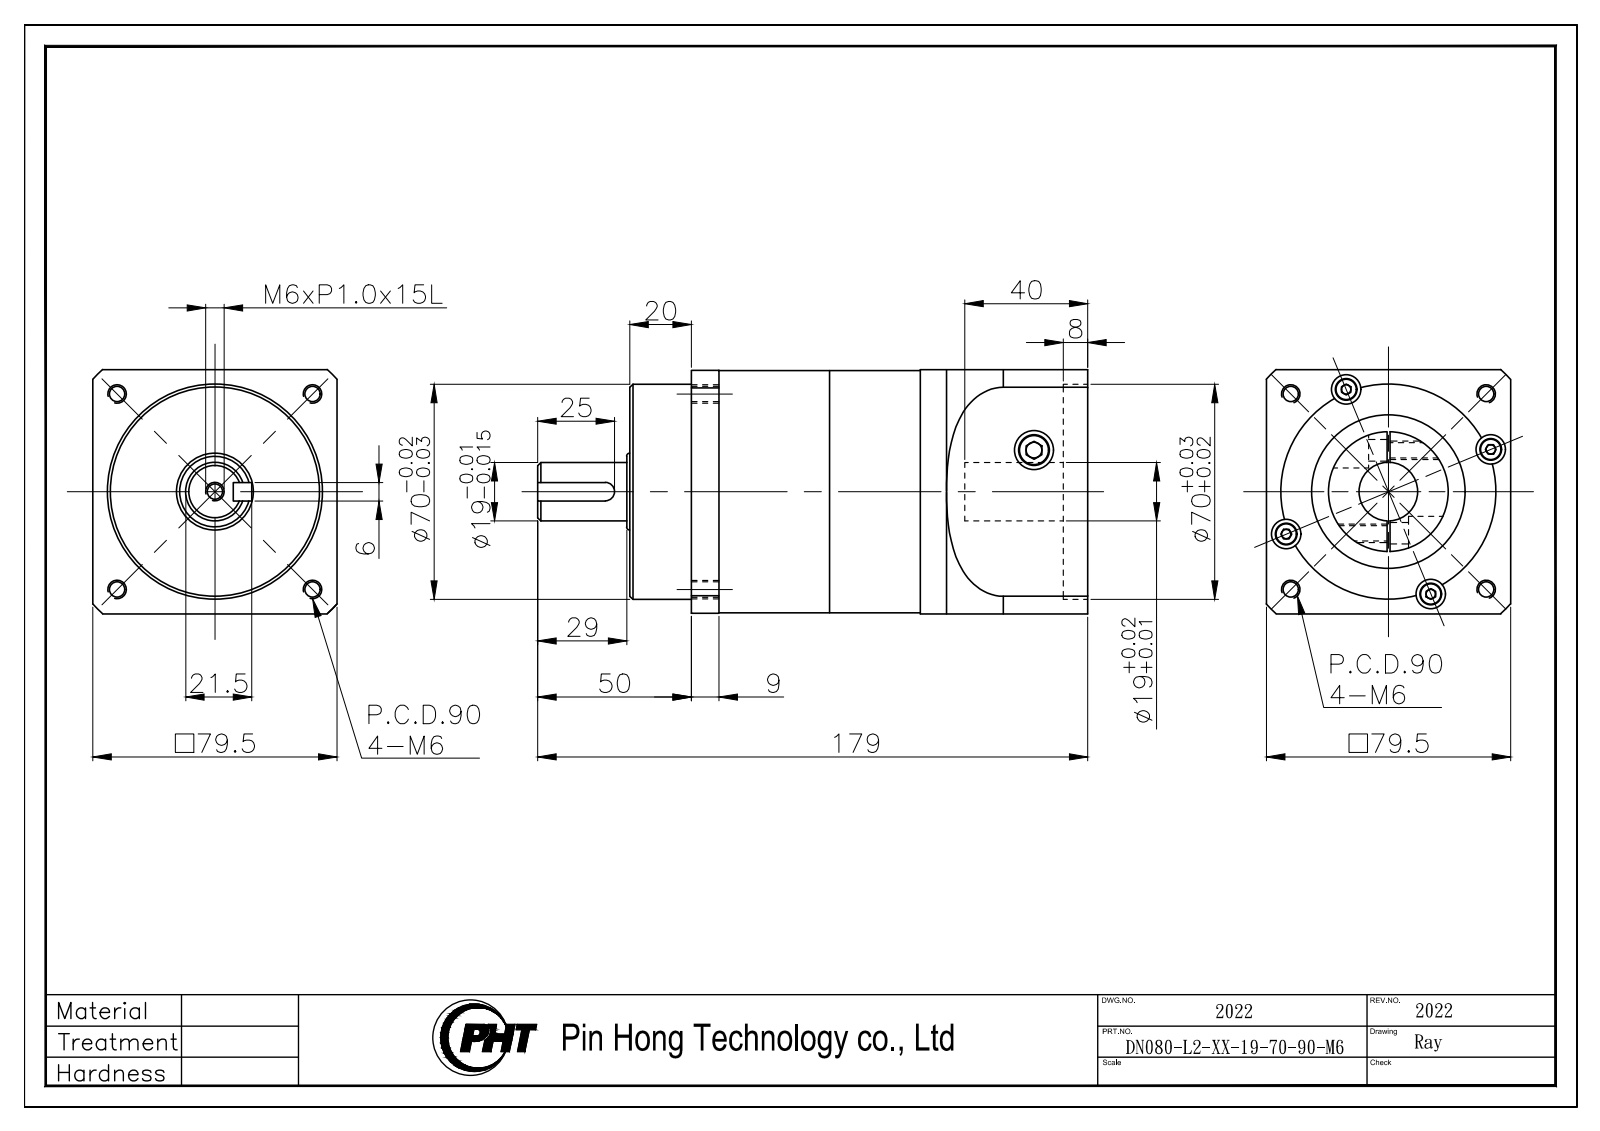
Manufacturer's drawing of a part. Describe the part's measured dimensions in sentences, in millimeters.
The part is named "DN080-L2-XX-19-70-90-M6_2022". Its 3-D file was written by "SolidWorks 2016 (AUTOMOTIVE_DESIGN)". It is 4 solids with 163 faces: 66 planar, 75 cylindrical and 22 other. Overall it measures 179 by 79.5 by 79.5 millimeters. Its volume is 709 800 cubic millimeters and its surface area 102 302 square millimeters. Round holes: 5 of diameter 5, 4 of diameter 9.5, 2 of diameter 12.7, 1 of diameter 19, 1 of diameter 50, 1 of diameter 70. Round bosses or shafts: 4 of diameter 8.5, 1 of diameter 79, 1 of diameter 78.8, 1 of diameter 39, 1 of diameter 25. Partial cylindrical surfaces (rounded edges, fillets, slot ends): 1 of radius 3, 1 of radius 54. The main face-to-face distances are 29.5, 79.5, 29, 36, 65.5, 65, 94.5, 45, 74.5, 20. The hole center spacings are 17.8, 36, 45, 45.91, 50.92, 63.64, 67.34, 79.53.
